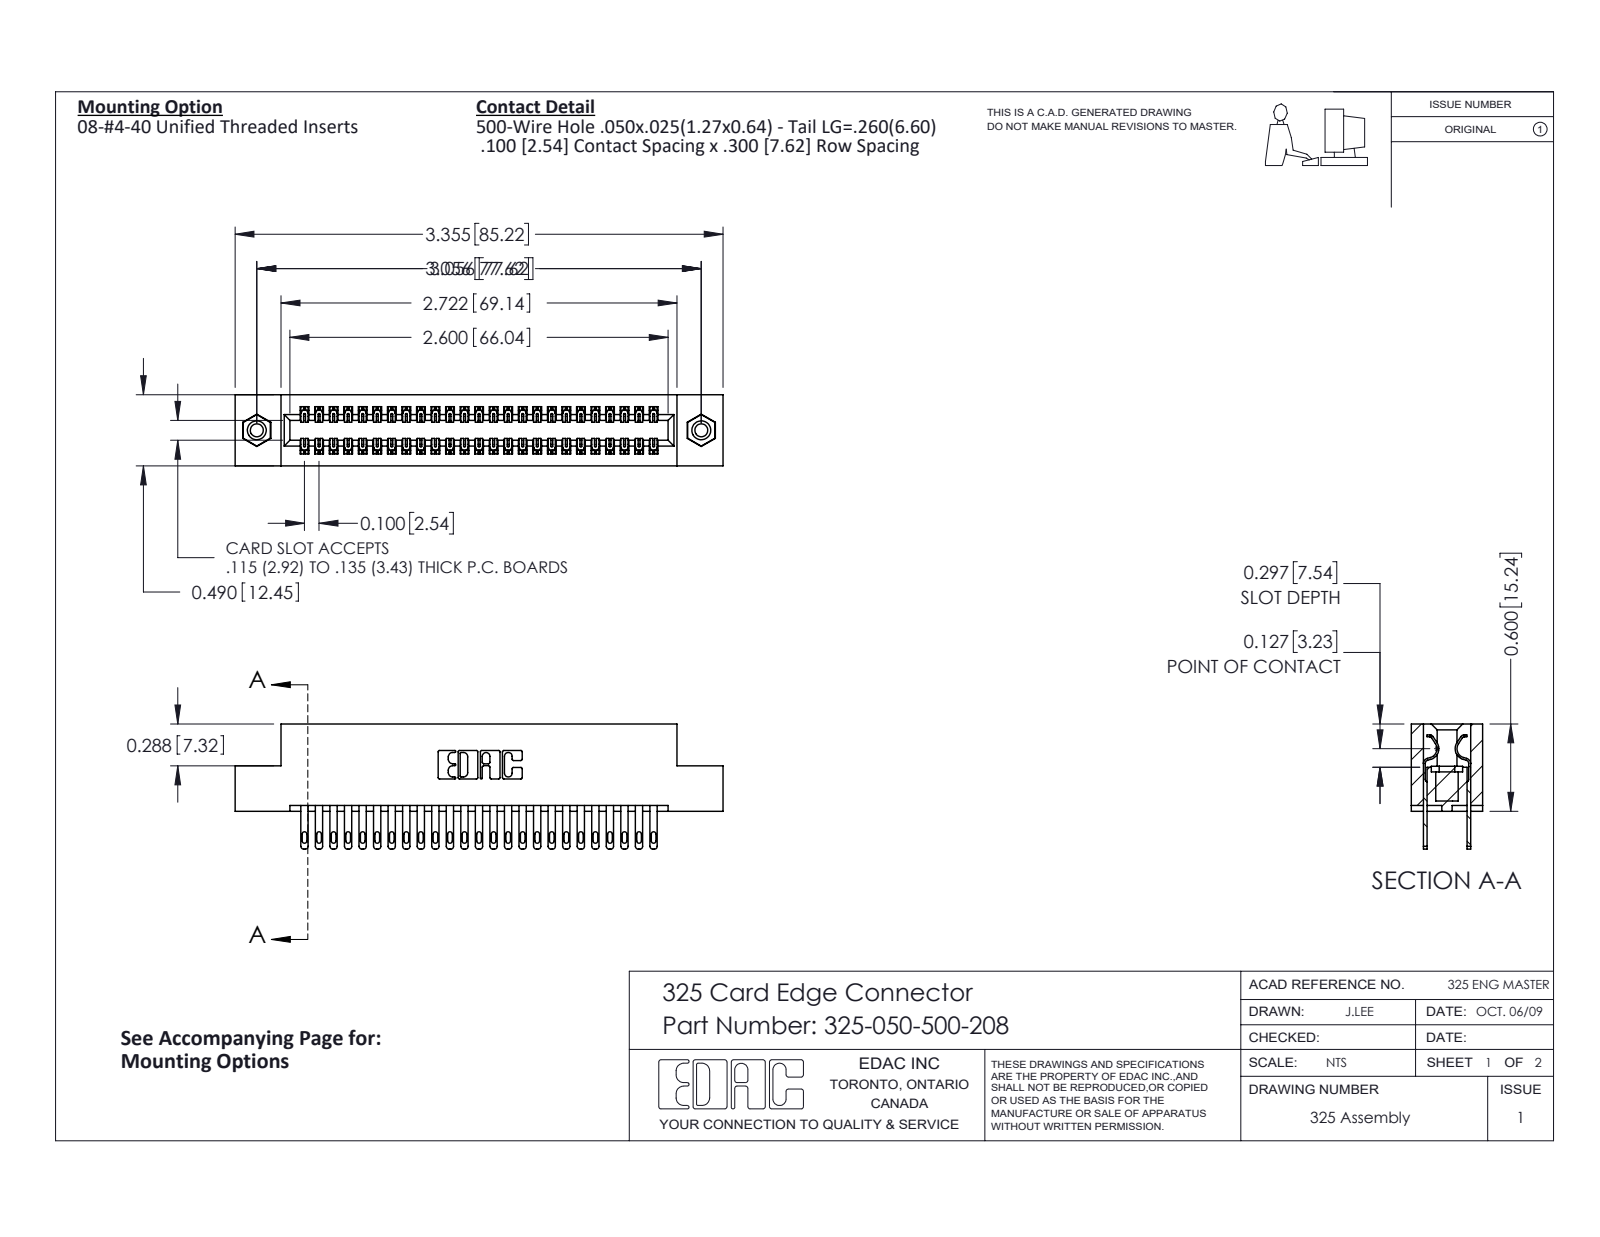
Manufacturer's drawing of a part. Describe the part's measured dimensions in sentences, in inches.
The part is named "345-250-001_345-250-003-102; 325-292-001_325-293-100; 325 Part_TI; 325-050-500-208". Its 3-D file was written by "SolidWorks 2016 (CONFIG_CONTROL_DESIGN)". It is 53 solids with 2574 faces: 1602 planar, 956 cylindrical and 16 other. Overall it measures 3.355 by 0.86 by 0.49 inches. Its volume is 0.671 cubic inches and its surface area 20.83 square inches. Round holes: 2 of diameter 0.089, 2 of diameter 0.125, 2 of diameter 0.16. Round bosses or shafts: 2 of diameter 0.155. Partial cylindrical surfaces (rounded edges, fillets, slot ends): 75 of radius 0.006, 50 of radius 0.016, 50 of radius 0.02, 22 of radius 0.01, 6 of radius 0.007, 6 of radius 0.031, 3 of radius 0.026, 2 of radius 0.014. The main face-to-face distances are 0.083, 0.407, 0.3, 0.107, 0.383, 0.025, 0.49, 0.325, 0.275, 0.04. The hole center spacings are 3.056.
